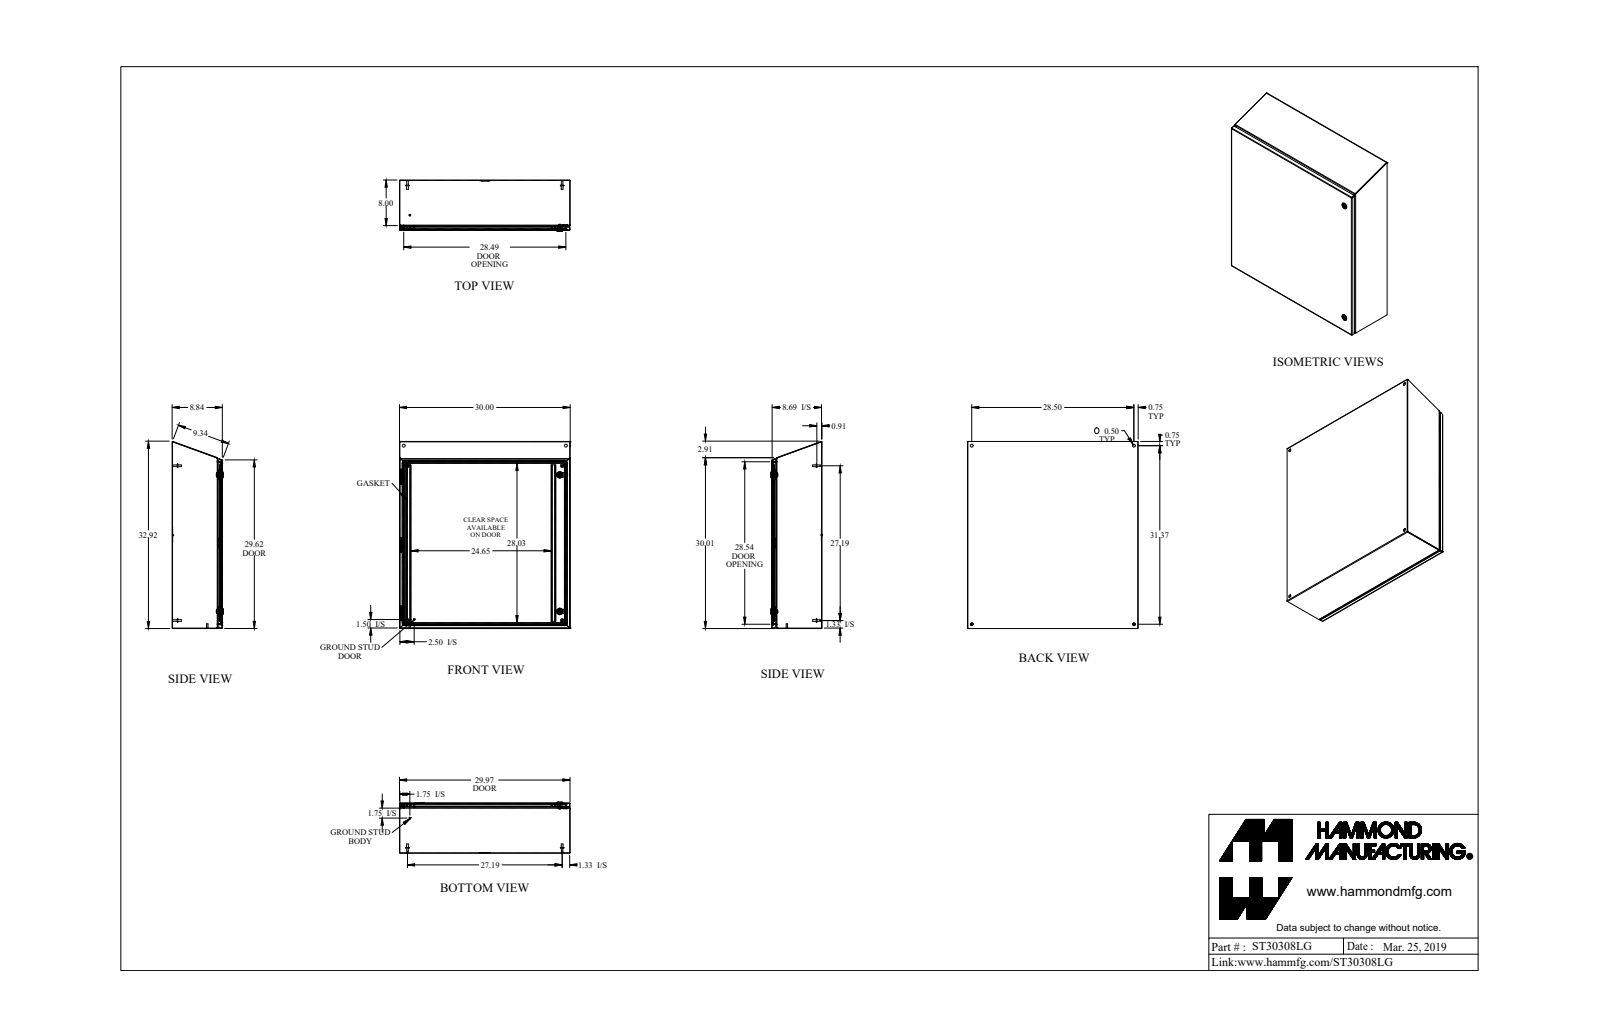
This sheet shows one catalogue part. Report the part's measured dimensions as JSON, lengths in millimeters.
{"part_name": "ST30308LG", "step_written_by": "SolidWorks 2018 (AUTOMOTIVE_DESIGN)", "units": "millimeters", "bodies": {"solids": 33, "faces": 868, "planar": 430, "cylindrical": 278, "other": 160}, "overall_size": [834.9, 762, 228.5], "volume_mm3": 3917000, "surface_area_mm2": 4323000, "round_holes": [[12.7, 4], [4.4, 2], [5.9, 2], [6.1, 2], [15.9, 2], [19.9, 2], [6.1, 1]], "round_bosses_or_shafts": [[15.9, 4], [8, 4], [6.9, 4], [27.9, 2], [13.3, 2], [9, 2], [7.4, 2], [7.1, 2]], "partial_cylinders_radius": [[0.9, 18], [2.7, 18], [1.1, 12], [2.1, 12], [0.2, 6], [1.6, 6], [4.8, 5], [3.2, 4]], "face_to_face_distances": [1.8, 222.6, 220.8, 224.5, 760.2, 758.3, 762, 201.4, 21.3, 203.2], "hole_center_spacings": [723.9, 796.8, 1076.6, 63.3, 132.9, 609.6, 667.3, 699]}
